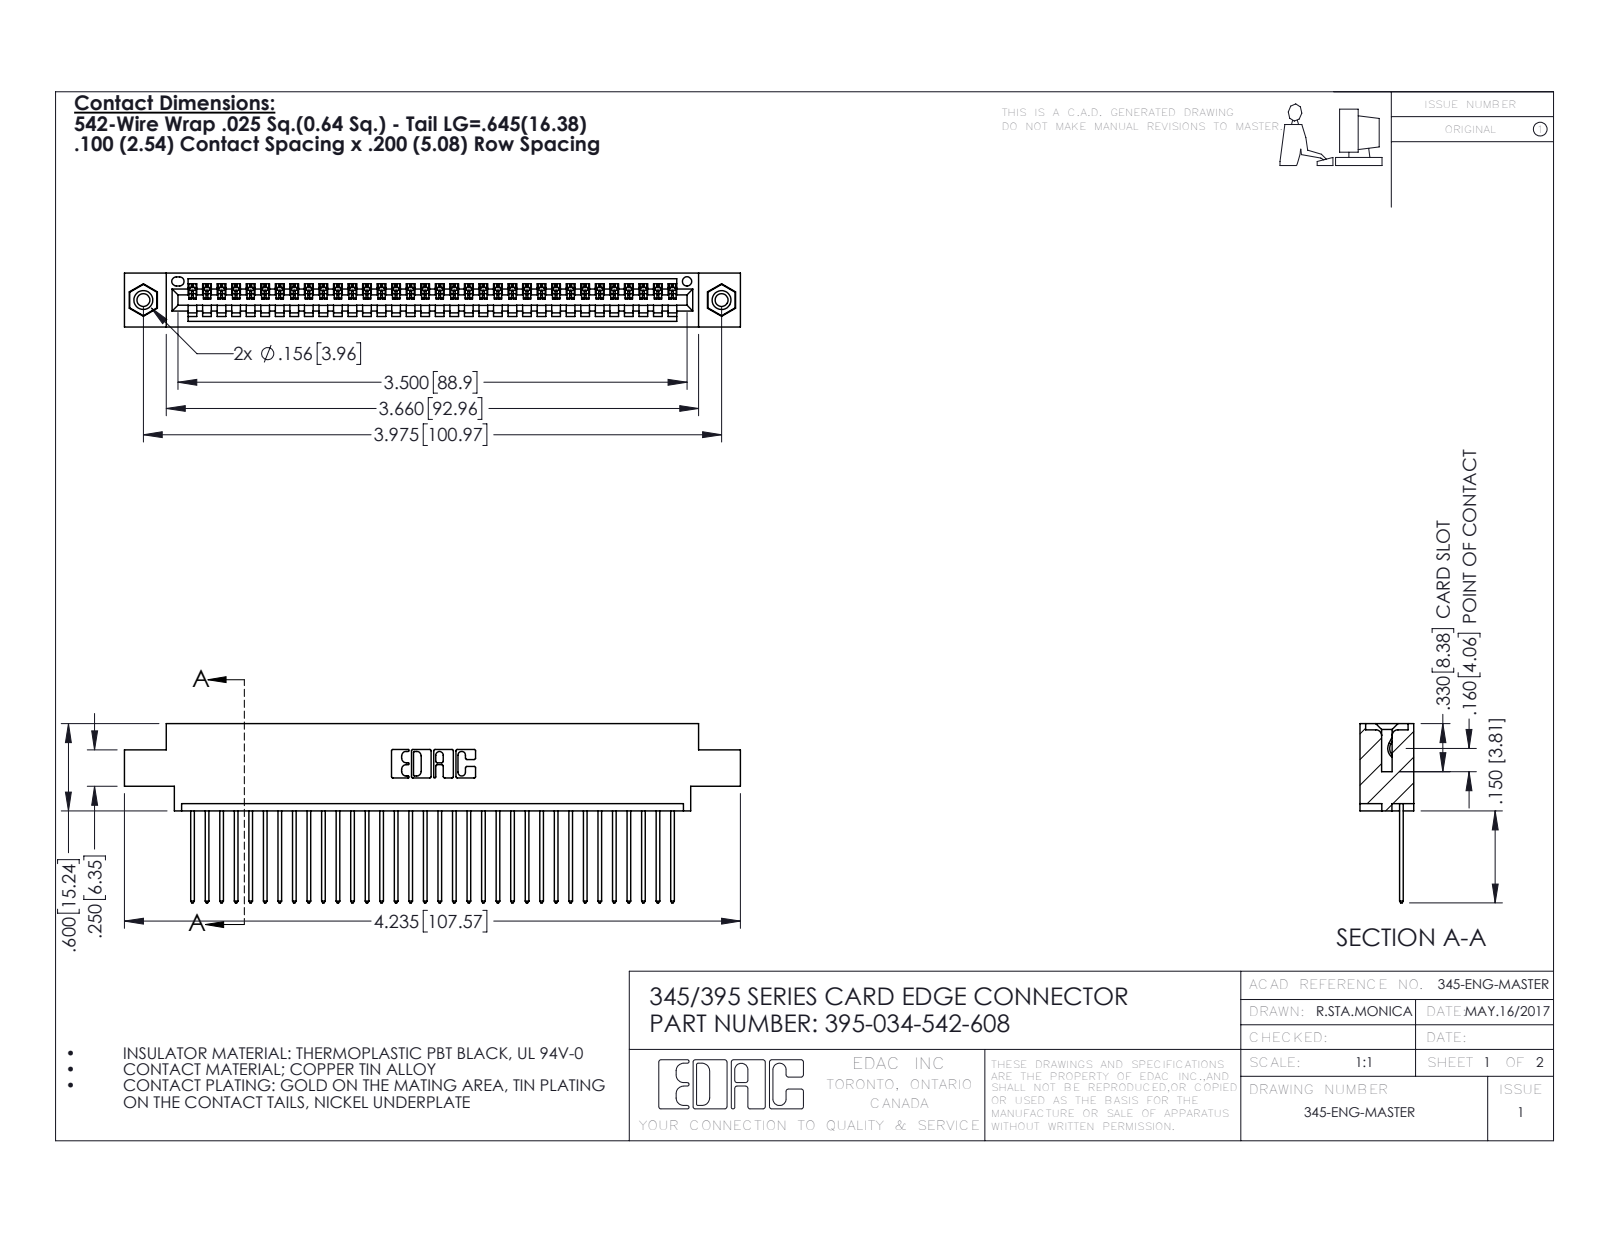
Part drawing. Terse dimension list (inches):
name: 345 Part_0.170 Offset - 0.156 Dia-TI; 345-292-001_345-293-142; 345-250-001_345-250-003-102; 395-034-542-608
written by: SolidWorks 2016 (CONFIG_CONTROL_DESIGN)
unit: in
bodies: 37 solids, 2162 faces (1476 planar, 670 cylindrical, 16 other)
size: 4.235 × 1.232 × 0.37
volume: 0.617 in³; area: 21.62 in²
holes: 2× ⌀0.089, 2× ⌀0.125, 2× ⌀0.156, 1× ⌀0.064
bosses: 2× ⌀0.155
rounds: 68× R0.006, 68× R0.01, 22× R0.01, 6× R0.007, 6× R0.031, 3× R0.026, 2× R0.031, 2× R0.04
face distances: 0.072, 0.298, 0.37, 0.098, 0.272, 0.025, 0.2, 0.225, 0.175, 0.149
hole spacings: 0.27, 3.74, 3.975
